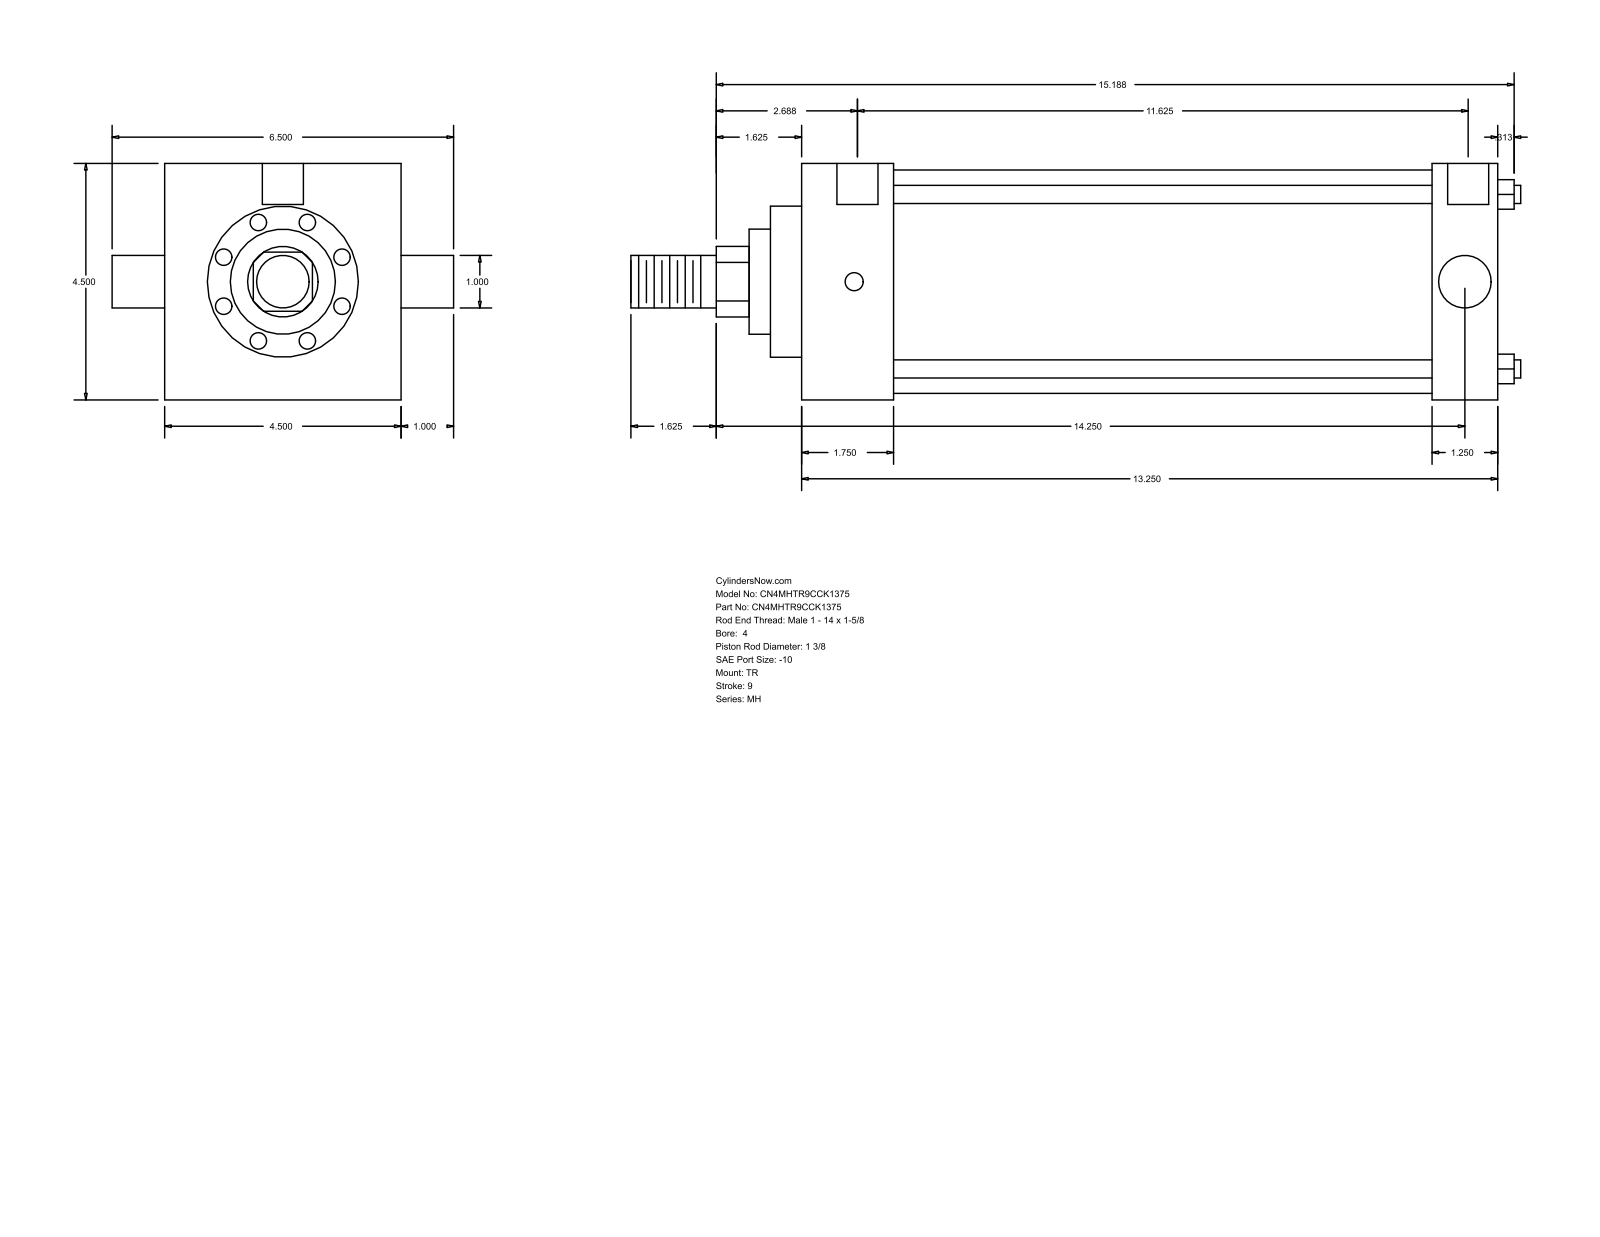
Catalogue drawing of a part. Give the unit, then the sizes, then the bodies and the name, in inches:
Units: inches
Overall size (bounding box): 16.937 × 6.5 × 4.5
Round holes (diameter × count): ⌀0.344 ×3, ⌀0.781 ×2
Round bosses / shafts (diameter × count): ⌀0.345 ×4, ⌀1 ×2, ⌀4.25 ×1, ⌀2.875 ×1, ⌀2 ×1, ⌀1.375 ×1
Partial cylindrical surfaces — rounded edges, fillets, slot ends (radius × count): R0.672 ×1
Main face-to-face distances: 4.5, 13.25, 1.75, 11.5, 12, 10.25, 1.25, 0.594, 2.344, 12.594
Hole centre spacings: 0.062, 0.063, 11.625, 11.687, 11.688, 11.75
Bodies: 0 solids, 86 faces (61 planar, 25 cylindrical, 0 other)
Part name (STEP PRODUCT): MH_TR__0400_1.375
STEP written by: GSSL Pune (CONFIG_CONTROL_DESIGN)
